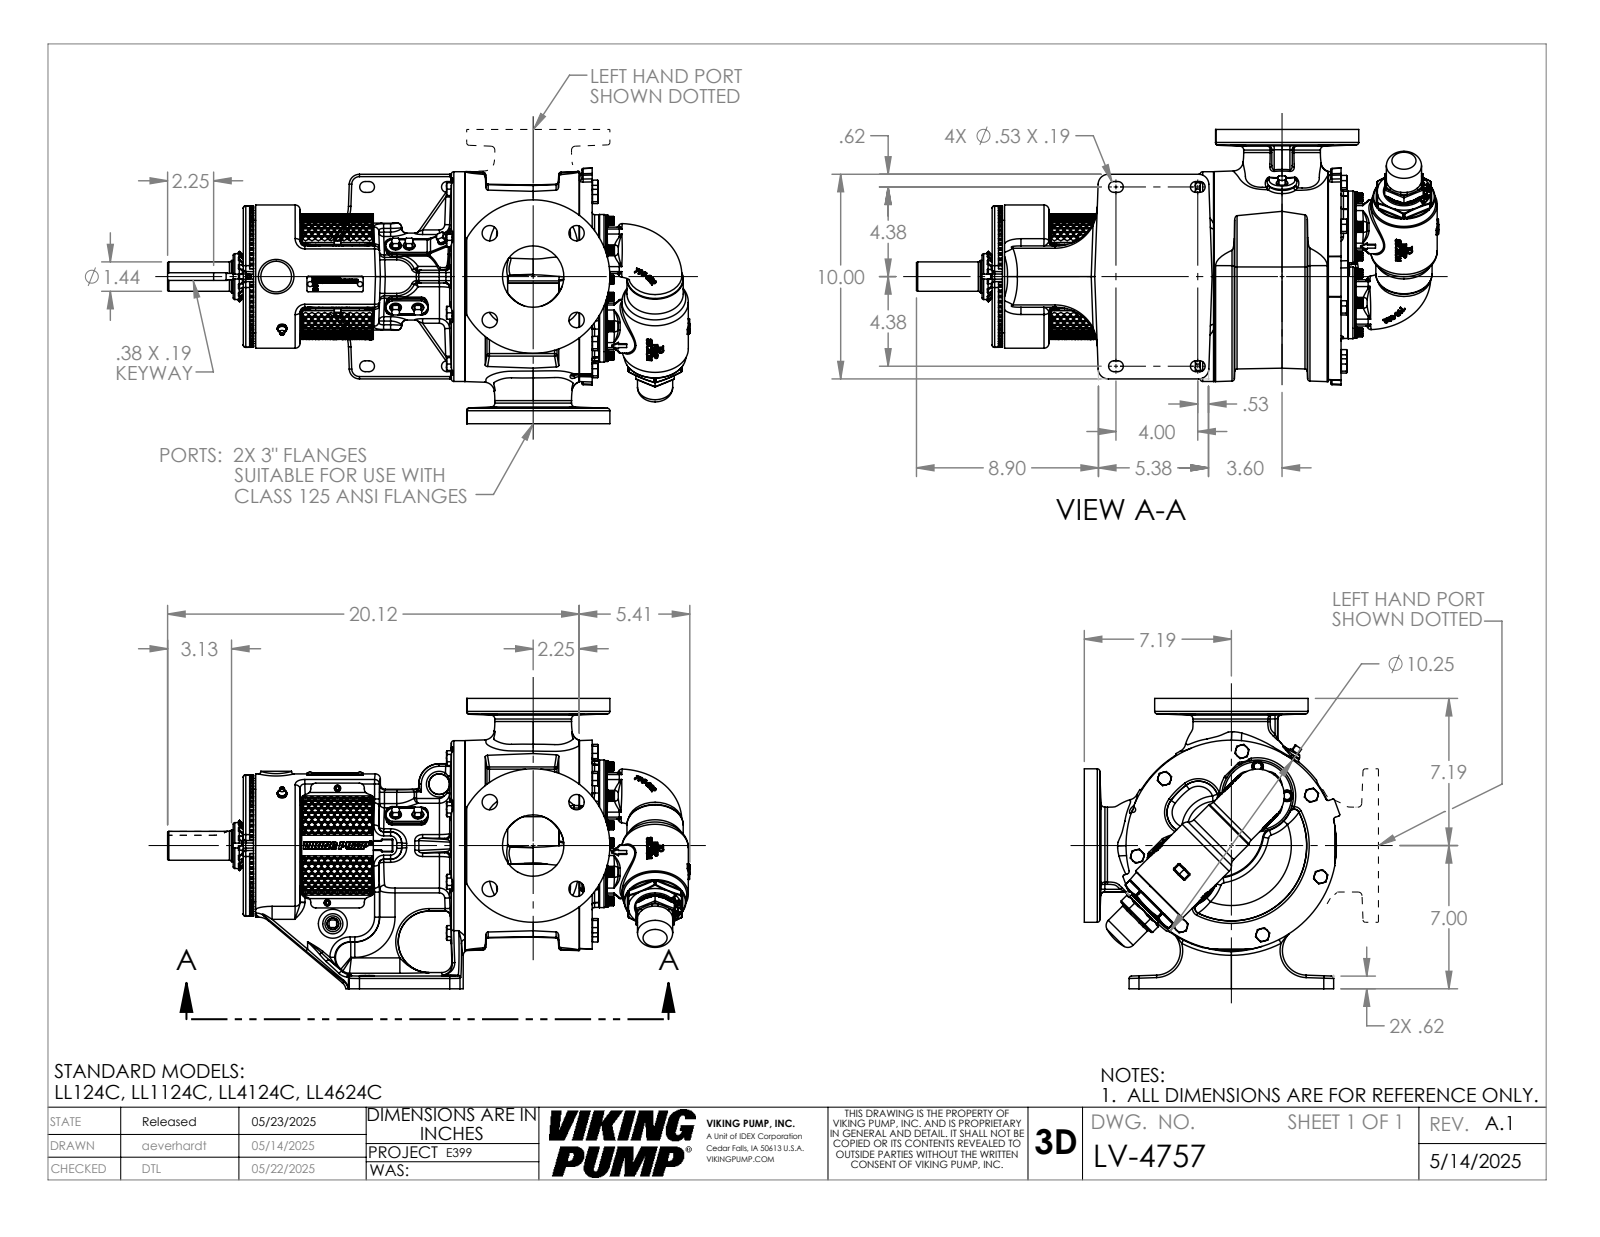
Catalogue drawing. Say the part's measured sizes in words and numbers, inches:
The part is named "LV-4757". Its 3-D file was written by "SolidWorks 2024 (AUTOMOTIVE_DESIGN)". It is 1 solid with 5337 faces: 1761 planar, 1136 cylindrical and 2440 other. Overall it measures 25.53 by 14.19 by 12.492 inches. Its volume is 962.6 cubic inches and its surface area 1 465 square inches. Round holes: 8 of diameter 0.406, 8 of diameter 0.41, 8 of diameter 0.75, 8 of diameter 1.094, 6 of diameter 0.199, 6 of diameter 0.25, 3 of diameter 0.159, 2 of diameter 0.266, 2 of diameter 0.313, 1 of diameter 0.453, 1 of diameter 1.552, 1 of diameter 1.577. Round bosses or shafts: 11 of diameter 0.625, 8 of diameter 0.563, 5 of diameter 0.375, 4 of diameter 0.625, 3 of diameter 0.437, 3 of diameter 0.375, 3 of diameter 0.312, 2 of diameter 7.5. Partial cylindrical surfaces (rounded edges, fillets, slot ends): 109 of radius 0.063, 99 of radius 0.12, 74 of radius 0.069, 48 of radius 0.24, 36 of radius 0.03, 16 of radius 0.45, 14 of radius 0.75, 12 of radius 0.06. The main face-to-face distances are 14.19, 14.307, 3.537, 10.77, 0.5, 2.25, 1.5, 2.143, 5.68, 16.45. The hole center spacings are 3, 4.243, 1.375, 3.609, 1.709, 2.18, 4.446, 4.625.
